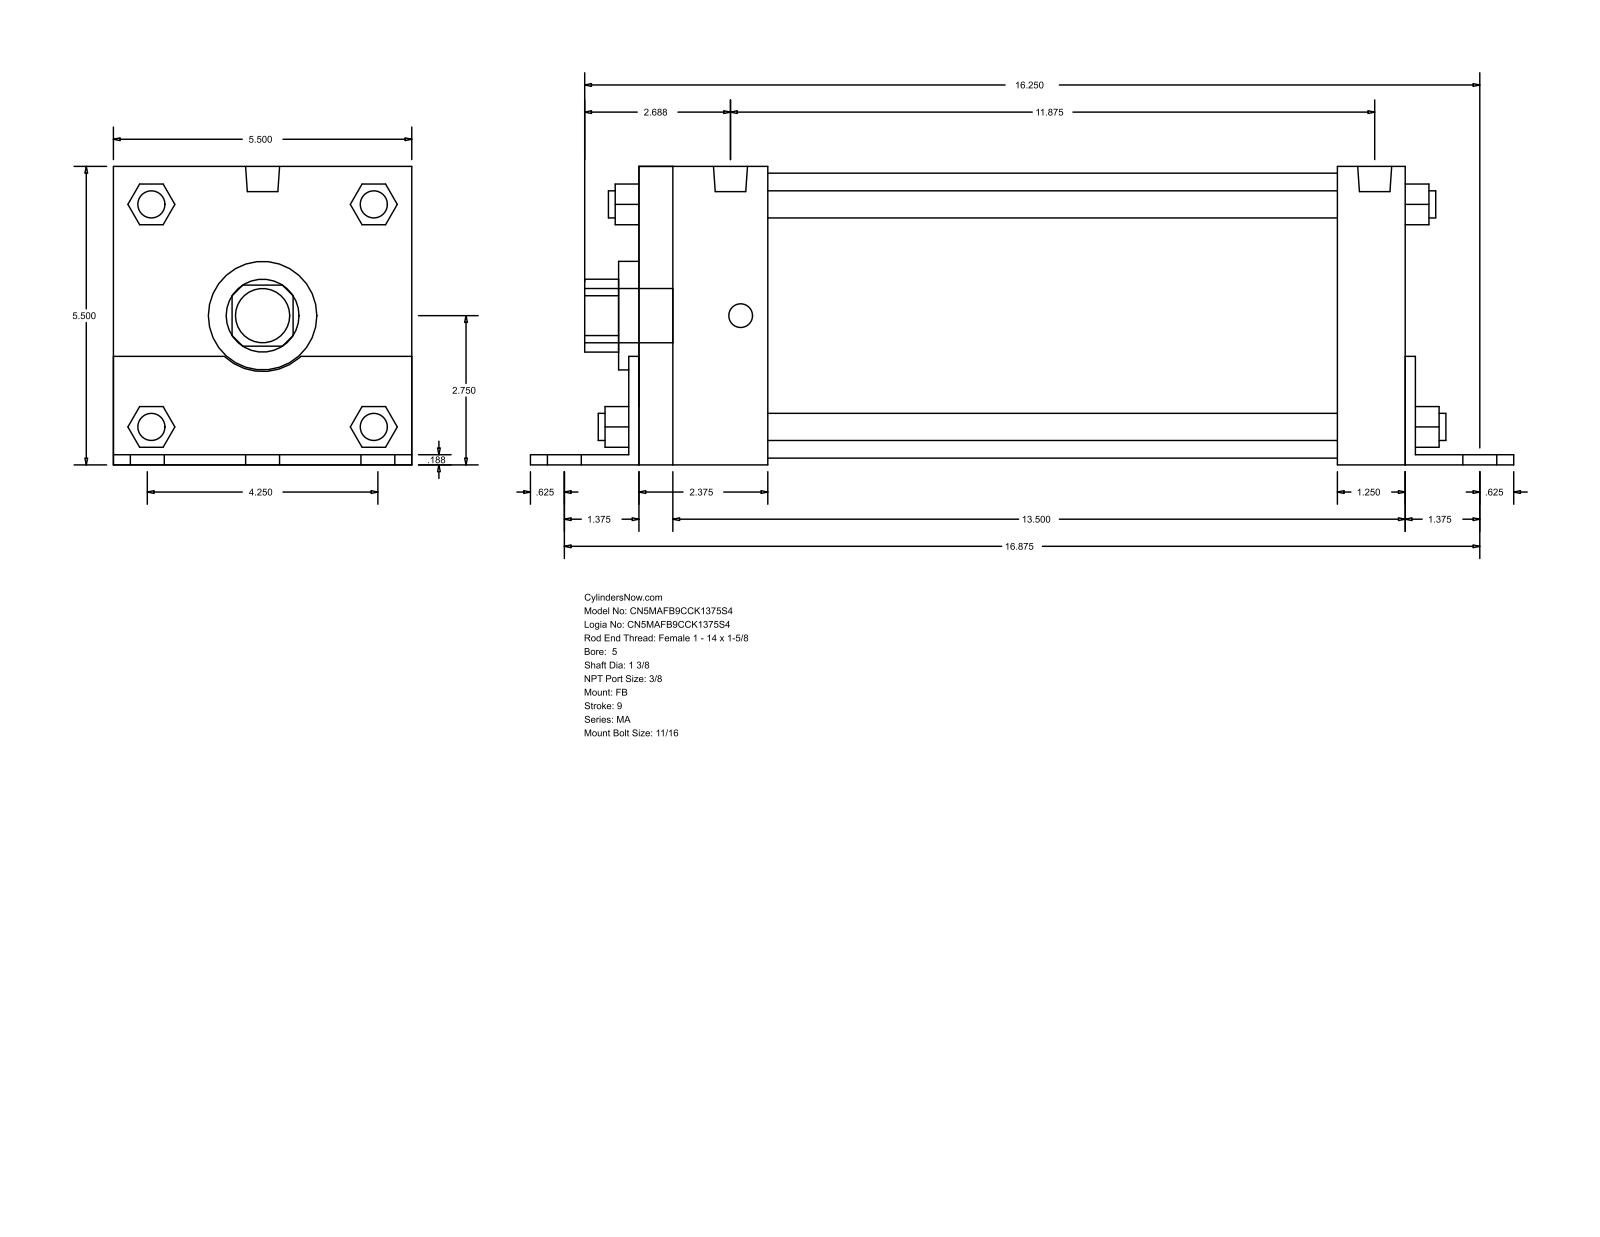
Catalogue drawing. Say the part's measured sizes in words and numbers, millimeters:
The part is named "MA_FB__0500_1.375". Its 3-D file was written by "GSSL Pune (CONFIG_CONTROL_DESIGN)". It is 0 solids with 140 faces: 105 planar, 35 cylindrical and 0 other. Overall it measures 460.38 by 139.75 by 139.7 millimeters. Round holes: 1 of diameter 34.92, 1 of diameter 50.8, 1 of diameter 133.35. Round bosses or shafts: 6 of diameter 17.46, 4 of diameter 12.7, 4 of diameter 11.11, 2 of diameter 15.93, 1 of diameter 25.4. Partial cylindrical surfaces (rounded edges, fillets, slot ends): 1 of radius 17.06, 1 of radius 26.16. The main face-to-face distances are 139.7, 4.76, 139.75, 363.54, 4.71, 134.99, 358.78, 368.3, 31.75, 36.51.
